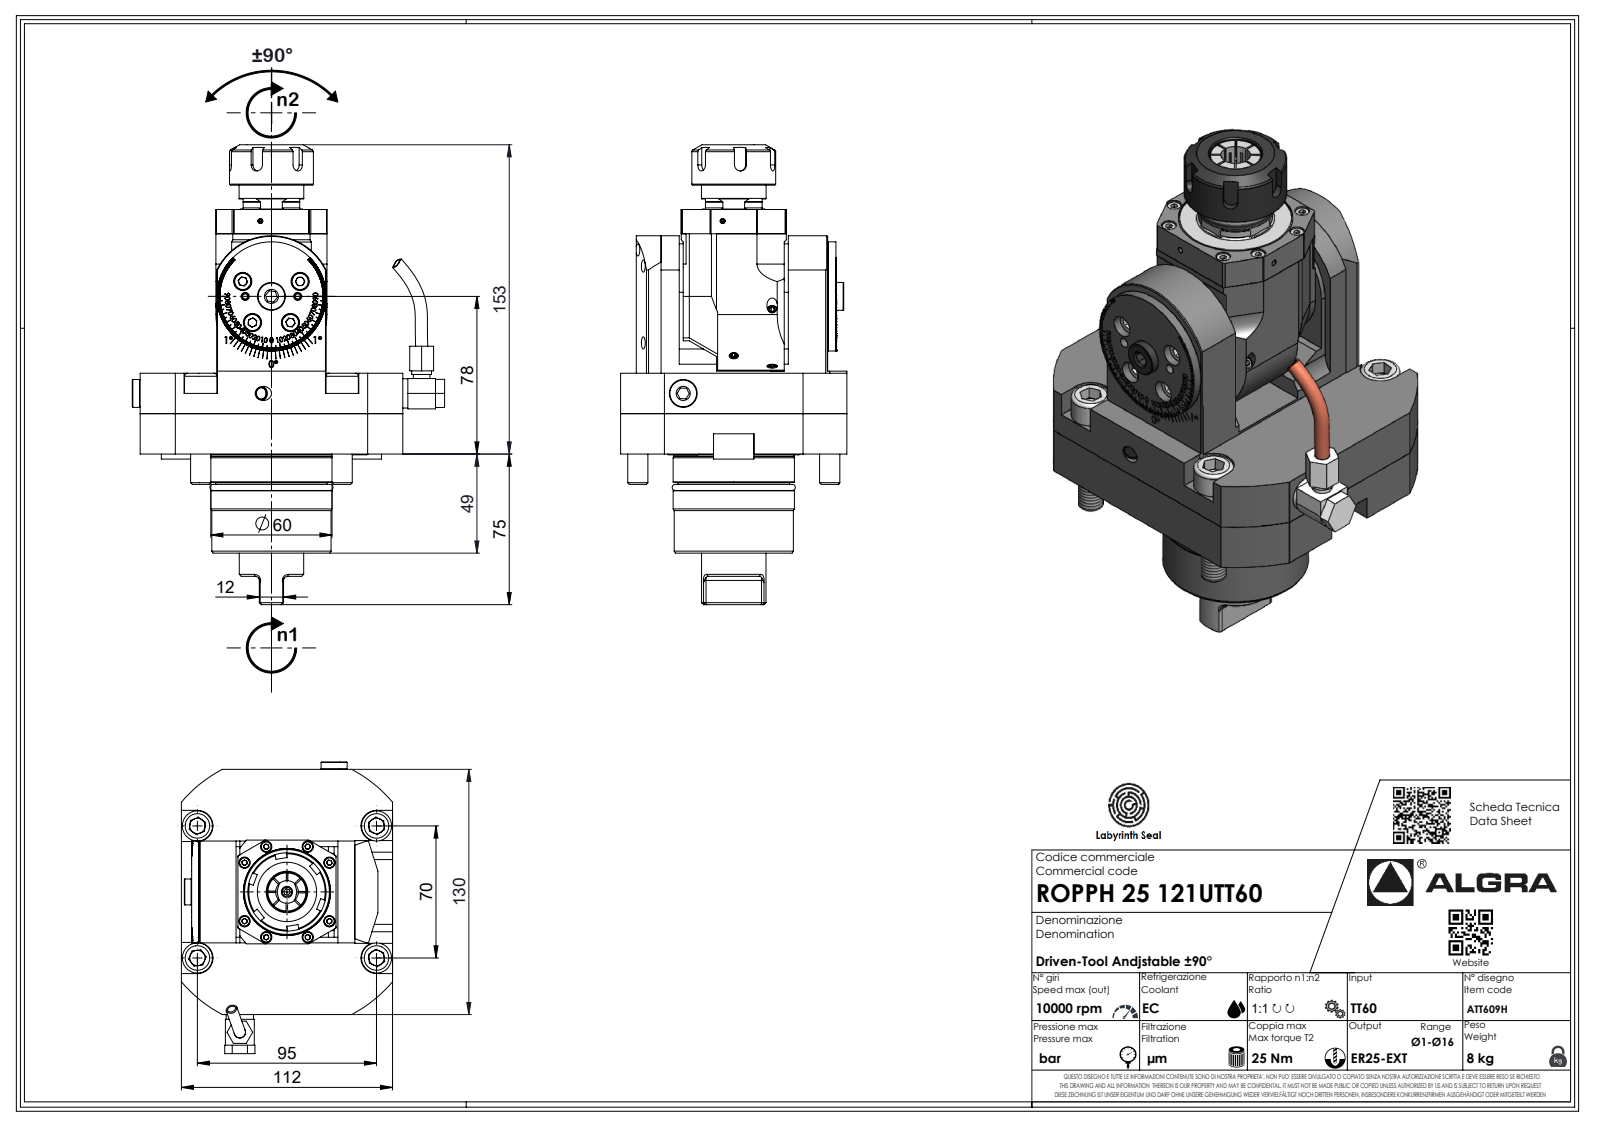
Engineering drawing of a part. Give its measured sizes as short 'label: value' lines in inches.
name: ROPPH25121UTT60
written by: SolidWorks 2023 (AUTOMOTIVE_DESIGN)
unit: in
bodies: 1 solid, 642 faces (415 planar, 118 cylindrical, 109 other)
size: 8.958 × 5.933 × 4.409
volume: 65.72 in³; area: 156.1 in²
holes: 1× ⌀0.083
bosses: 1× ⌀2.362, 1× ⌀2.354, 1× ⌀2.323, 1× ⌀2.173, 1× ⌀2.126, 1× ⌀1.634, 1× ⌀1.26, 1× ⌀1.256
rounds: 14× R0.079, 8× R0.039, 7× R0.013, 7× R0.02, 7× R0.146, 6× R0.394, 5× R0.118, 4× R0.197
face distances: 1.575, 0.039, 1.496, 3.622, 2.146, 0.02, 3.189, 1.476, 1.614, 2.126
